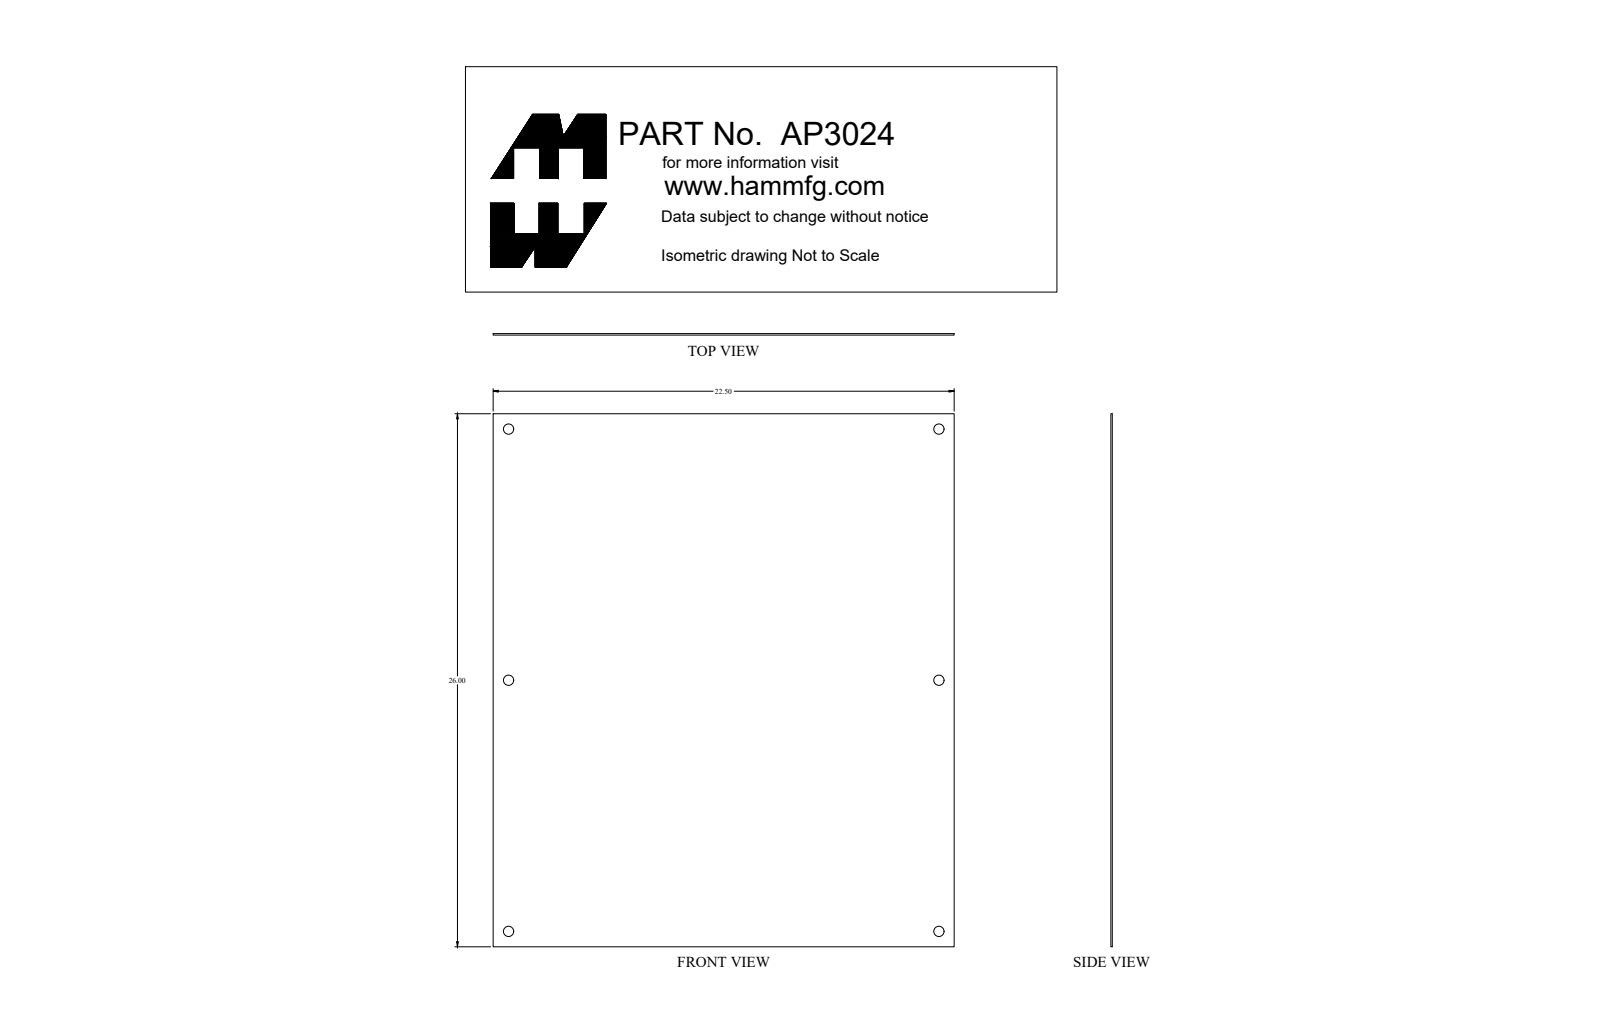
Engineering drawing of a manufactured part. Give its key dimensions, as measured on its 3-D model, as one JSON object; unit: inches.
{"part_name": "AP3024_Default", "step_written_by": "SolidWorks 2019 (CONFIG_CONTROL_DESIGN)", "units": "inches", "bodies": {"solids": 1, "faces": 18, "planar": 6, "cylindrical": 12, "other": 0}, "overall_size": [26, 22.5, 0.072], "volume_in3": 42.04, "surface_area_in2": 1175, "round_holes": [[0.5, 6]], "face_to_face_distances": [0.072, 22.5, 26], "hole_center_spacings": [12.25, 24.312, 21, 24.5, 32.269]}
